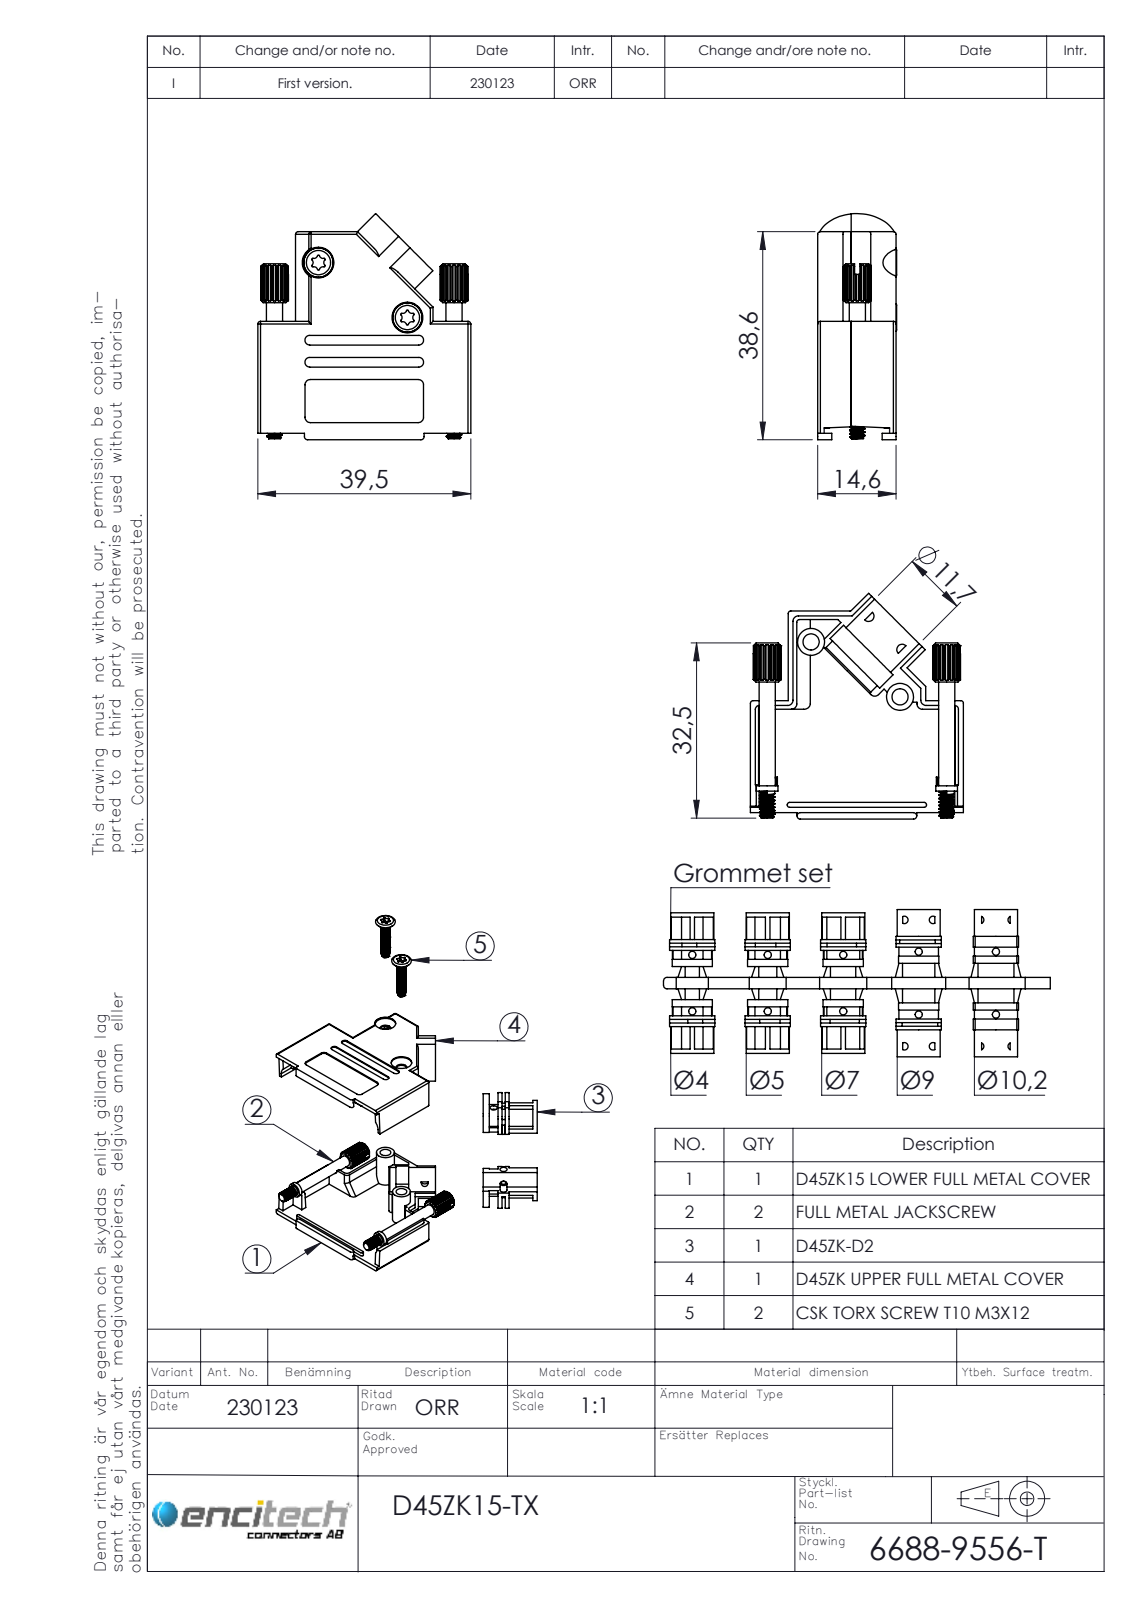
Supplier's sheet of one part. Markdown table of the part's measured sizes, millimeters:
| quantity | value |
| --- | --- |
| part name | 6826-0141-01; 6855-0117-12; 6805-0106-12; 6805-0106-02 (+2 more) |
| STEP written by | SolidWorks 2021 (AUTOMOTIVE_DESIGN) |
| units | millimeters |
| bodies | 8 solids, 819 faces (396 planar, 342 cylindrical, 81 other) |
| overall size | 42 × 39.5 × 14.65 |
| volume | 6 911 mm³ |
| surface area | 11 733 mm² |
| round holes (diameter × count) | 2 × 3, 3 × 2, 5.7 × 2, 7 × 1, 11.7 × 1 |
| round bosses / shafts (diameter × count) | 5 × 2, 4 × 2, 3 × 2, 2.85 × 2, 2.5 × 2, 1.9 × 2, 11.6 × 1, 9.2 × 1 |
| partial cylindrical surfaces (radius × count) | 0.5 × 28, 1 × 19, 0.18 × 12, 0.7 × 12, 0.4 × 6, 0.75 × 4, 0.9 × 4, 1.6 × 4 |
| main face-to-face distances | 1.2, 13.35, 12.15, 14.55, 0.9, 1.6, 14.25, 13.05, 37.9, 7 |
| hole center spacings | 5.71, 5.31, 5.81, 8.77, 10, 10.64, 14.32, 15.31 |
